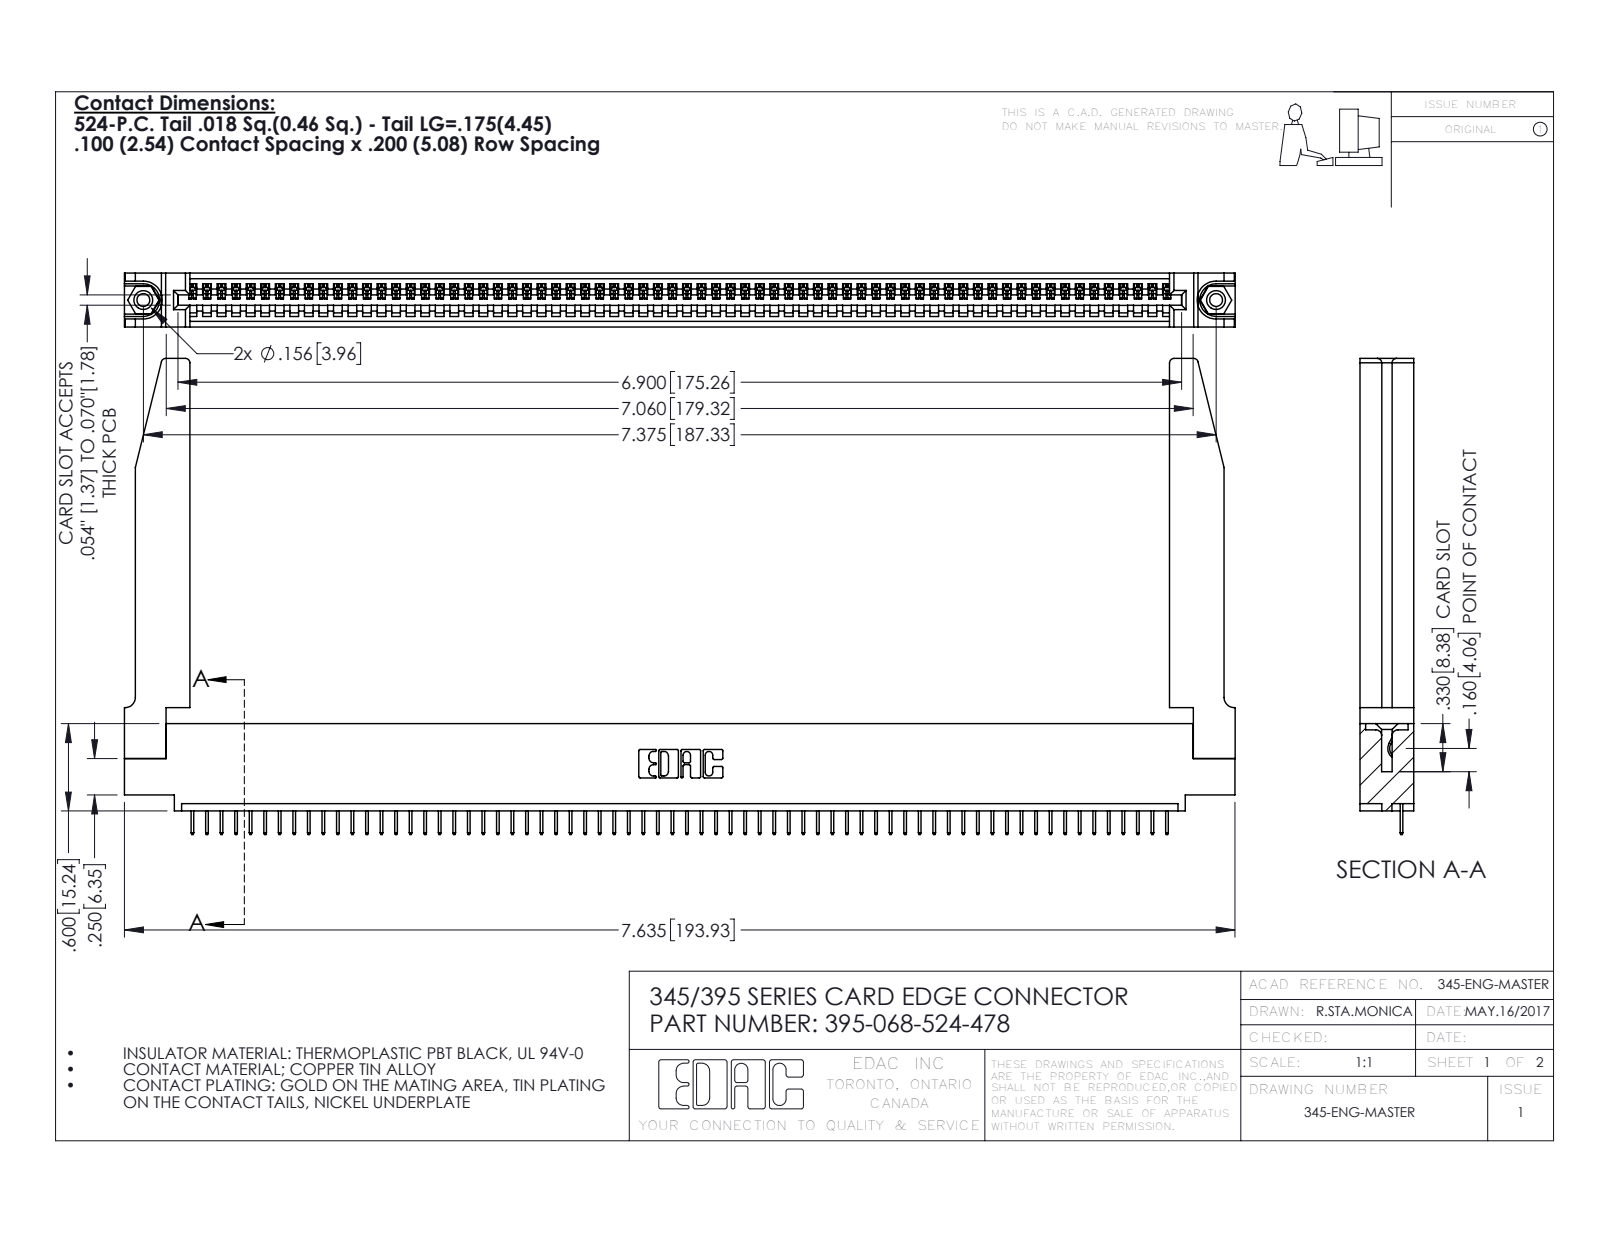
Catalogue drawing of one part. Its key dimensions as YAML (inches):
part_name: "345-220-078_345-220-078; 345 Part_0.110 Offset - 0.156 Dia-TH; 395-068-524-478; 345-292-001_345-293-124 (+1 more)"
step_written_by: "SolidWorks 2016 (CONFIG_CONTROL_DESIGN)"
units: inches
bodies: {solids: 73, faces: 4580, planar: 3354, cylindrical: 1174, other: 52}
overall_size: [7.636, 3.272, 0.37]
volume: 1.59
surface_area: 47.63
round_holes:
  - {diameter: 0.089, count: 2}
  - {diameter: 0.125, count: 2}
  - {diameter: 0.156, count: 2}
  - {diameter: 0.064, count: 1}
round_bosses_or_shafts:
  - {diameter: 0.155, count: 2}
partial_cylinders:
  - {radius: 0.006, count: 136}
  - {radius: 0.01, count: 22}
  - {radius: 0.03, count: 8}
  - {radius: 0.007, count: 6}
  - {radius: 0.031, count: 6}
  - {radius: 0.026, count: 3}
  - {radius: 0.031, count: 2}
  - {radius: 0.04, count: 2}
face_to_face_distances: [0.37, 0.072, 0.298, 0.098, 0.272, 0.025, 0.2, 0.225, 0.072, 0.149]
hole_center_spacings: [0.27, 7.139, 7.375]
